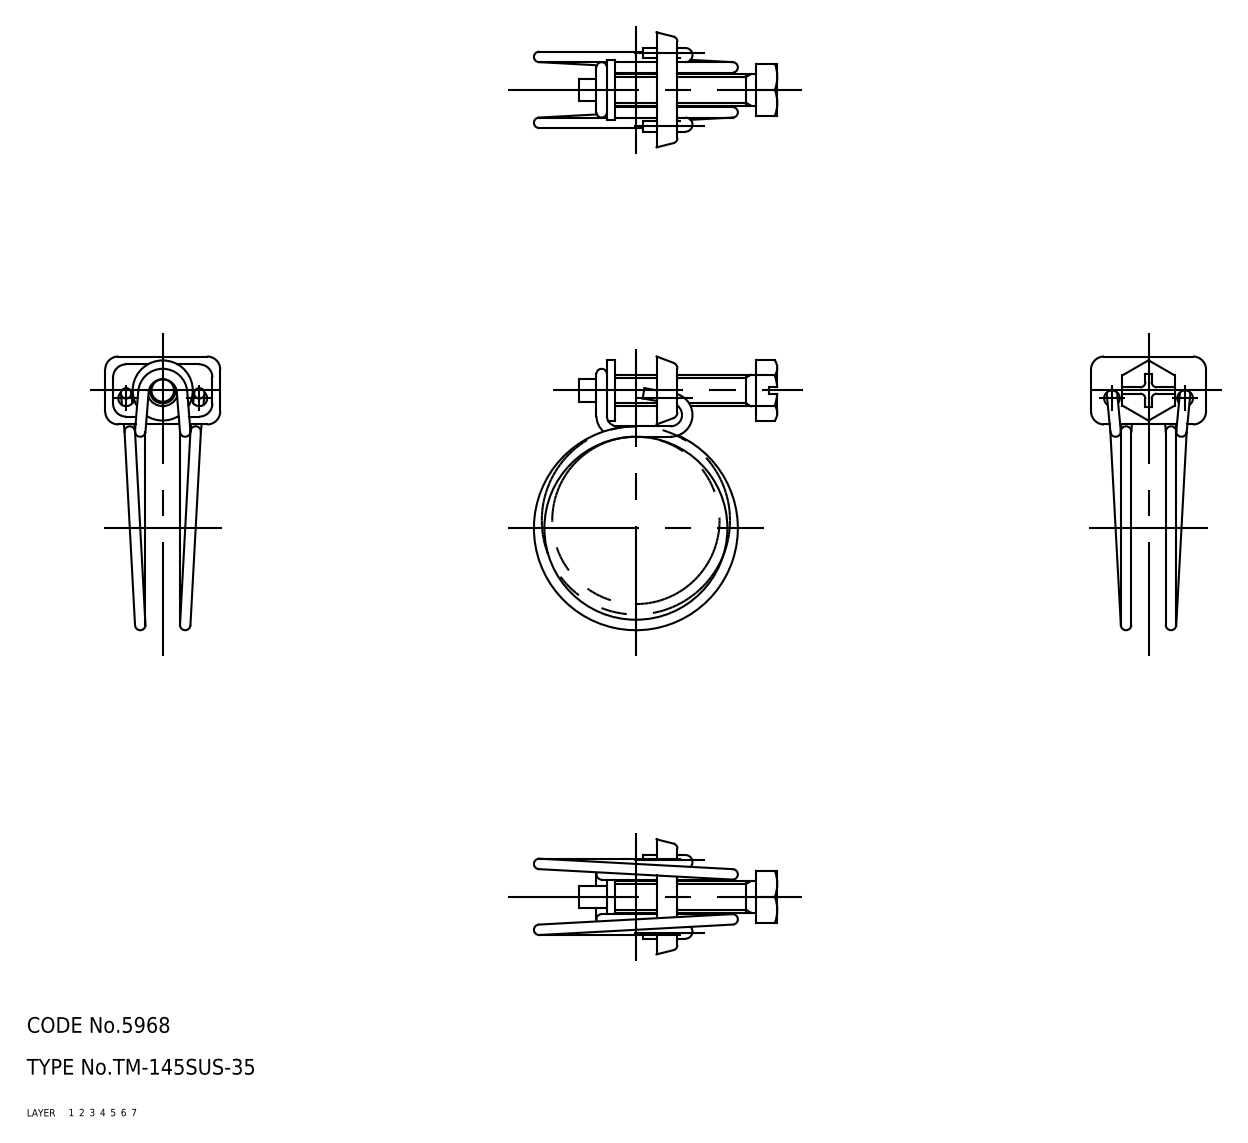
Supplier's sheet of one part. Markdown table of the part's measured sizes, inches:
| quantity | value |
| --- | --- |
| part name | screw; holder; band; TM_145SUS_35_22036_36 |
| STEP written by | CADfix (AUTOMOTIVE_DESIGN) |
| units | inches |
| bodies | 3 solids, 119 faces (0 planar, 0 cylindrical, 119 other) |
| overall size | 2.061 × 1.833 × 0.866 |
| volume | 0.171 in³ |
| surface area | 6.079 in² |
